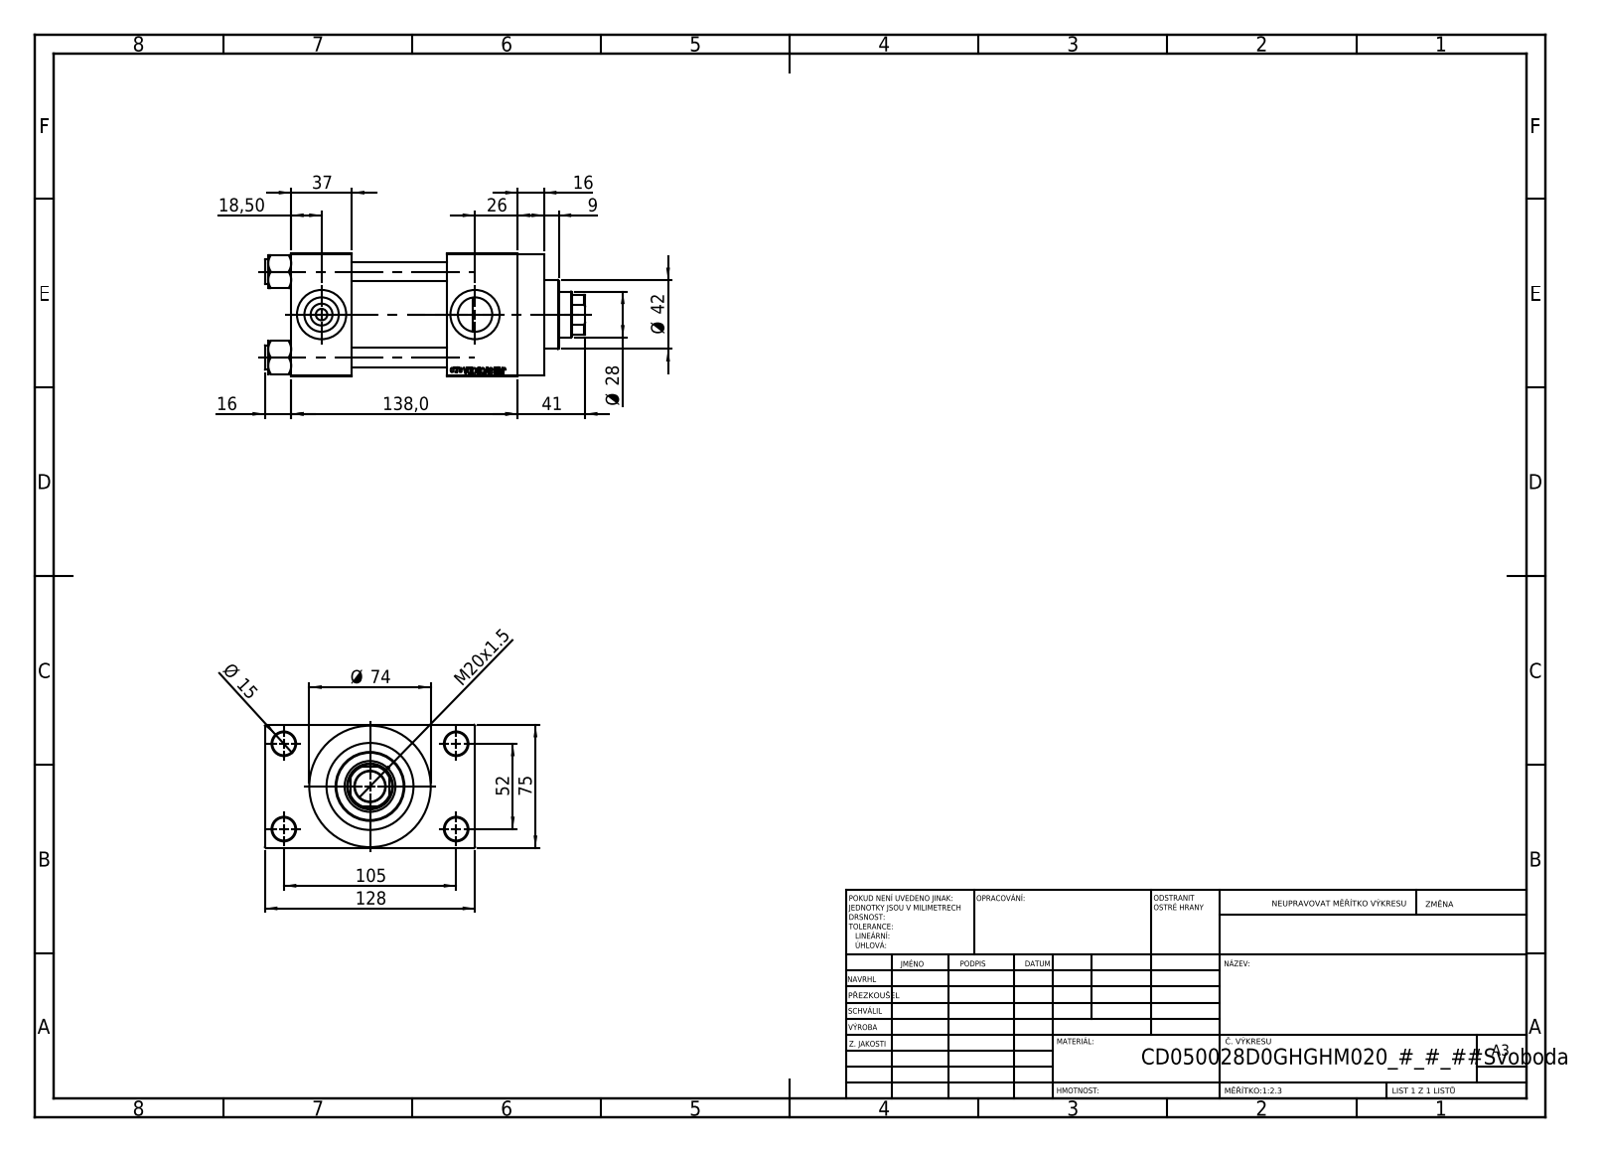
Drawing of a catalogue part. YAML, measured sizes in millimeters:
part_name: "V215CD_VCP_D; V215CD_NUT_M5_D; V215CD_D_Body; V215CD_VC_A (+1 more)"
step_written_by: "SolidWorks 2019 (CONFIG_CONTROL_DESIGN)"
units: millimeters
bodies: {solids: 11, faces: 1103, planar: 497, cylindrical: 88, other: 518}
overall_size: [195, 128, 75]
volume: 806210
surface_area: 170608
round_holes:
  - {diameter: 12, count: 4}
  - {diameter: 14, count: 4}
  - {diameter: 7, count: 2}
  - {diameter: 20.96, count: 2}
  - {diameter: 30, count: 2}
  - {diameter: 18.5, count: 1}
  - {diameter: 28, count: 1}
  - {diameter: 31, count: 1}
  - {diameter: 41, count: 1}
  - {diameter: 50, count: 1}
  - {diameter: 53, count: 1}
round_bosses_or_shafts:
  - {diameter: 15, count: 4}
  - {diameter: 74, count: 1}
  - {diameter: 56, count: 1}
  - {diameter: 42, count: 1}
partial_cylinders:
  - {radius: 13.5, count: 1}
face_to_face_distances: [75, 58, 37, 95, 26.5, 138, 101, 43, 101.5, 16]
hole_center_spacings: [26.35, 36.98, 52.3, 58.43, 58.59, 78.65, 94.37, 52]
